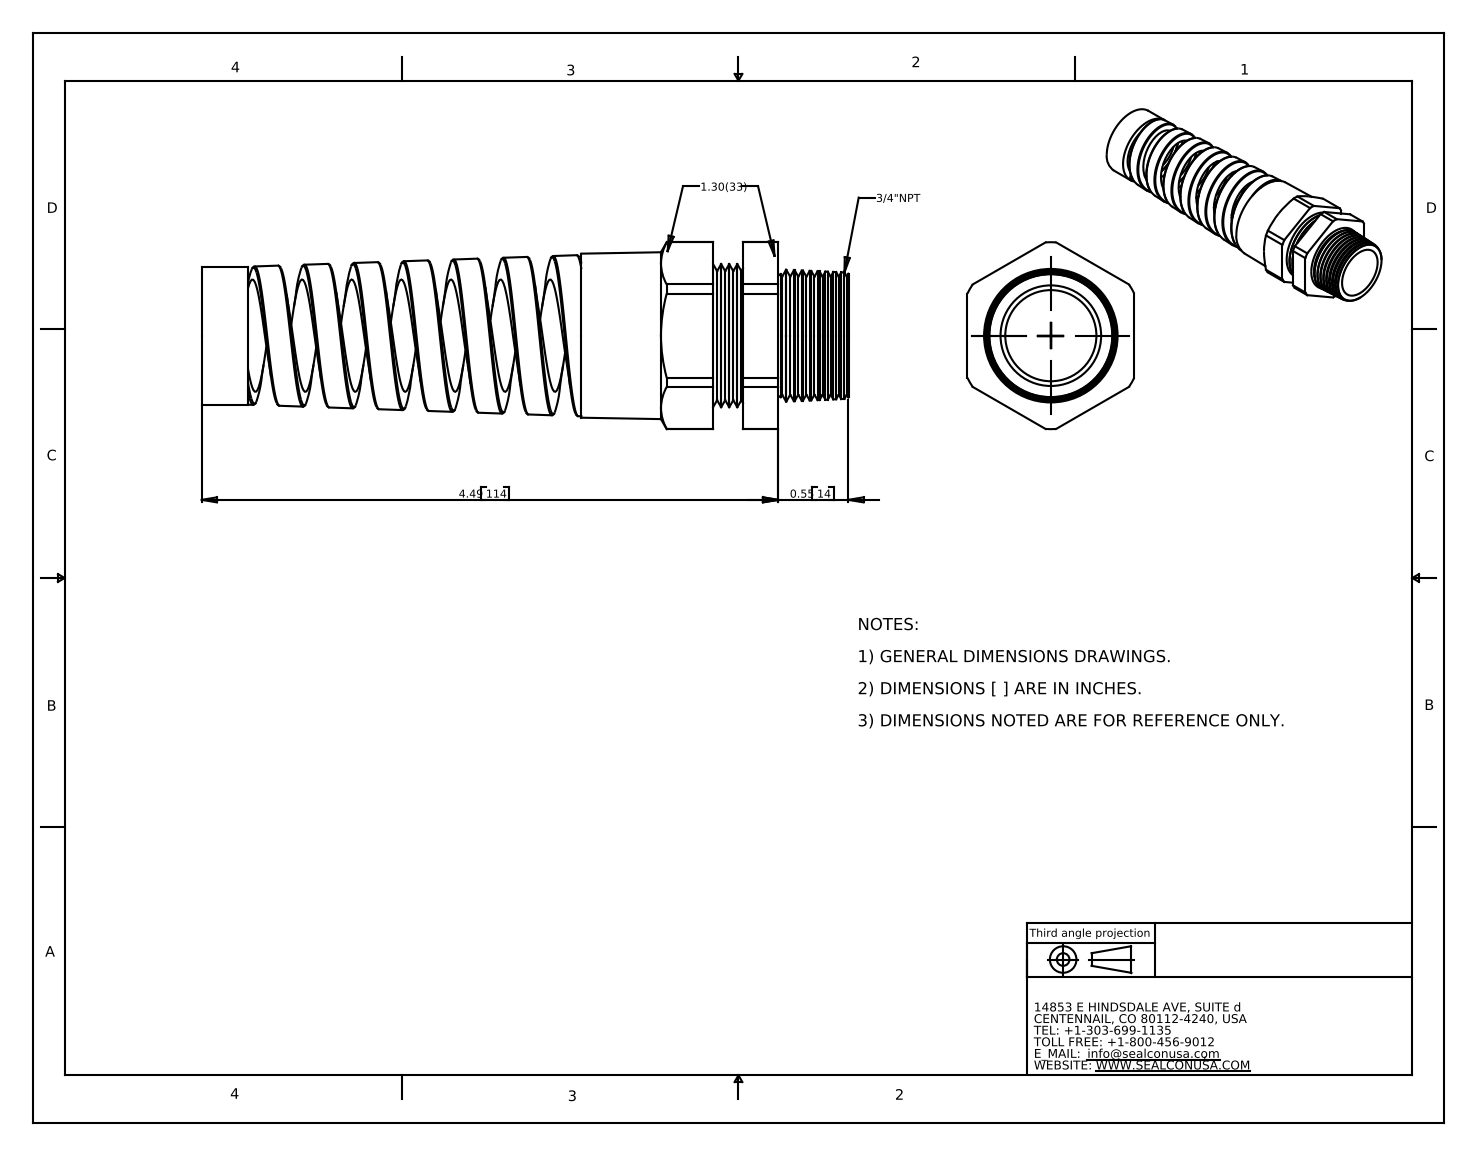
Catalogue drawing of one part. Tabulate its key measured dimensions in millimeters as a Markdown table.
| quantity | value |
| --- | --- |
| part name | CF21NA-GY |
| STEP written by | SolidWorks 2007 (CONFIG_CONTROL_DESIGN) |
| units | millimeters |
| bodies | 1 solid, 163 faces (19 planar, 39 cylindrical, 105 other) |
| overall size | 128 × 37 × 33 |
| volume | 37 660 mm³ |
| surface area | 22 900 mm² |
| round holes (diameter × count) | 18 × 1, 22.2 × 1 |
| round bosses / shafts (diameter × count) | 28.3 × 1, 27.3 × 1 |
| partial cylindrical surfaces (radius × count) | 18.5 × 1 |
| main face-to-face distances | 33, 38.9, 26.1, 12.9, 32, 5.9, 7, 75.1, 101.2, 107.1 |
